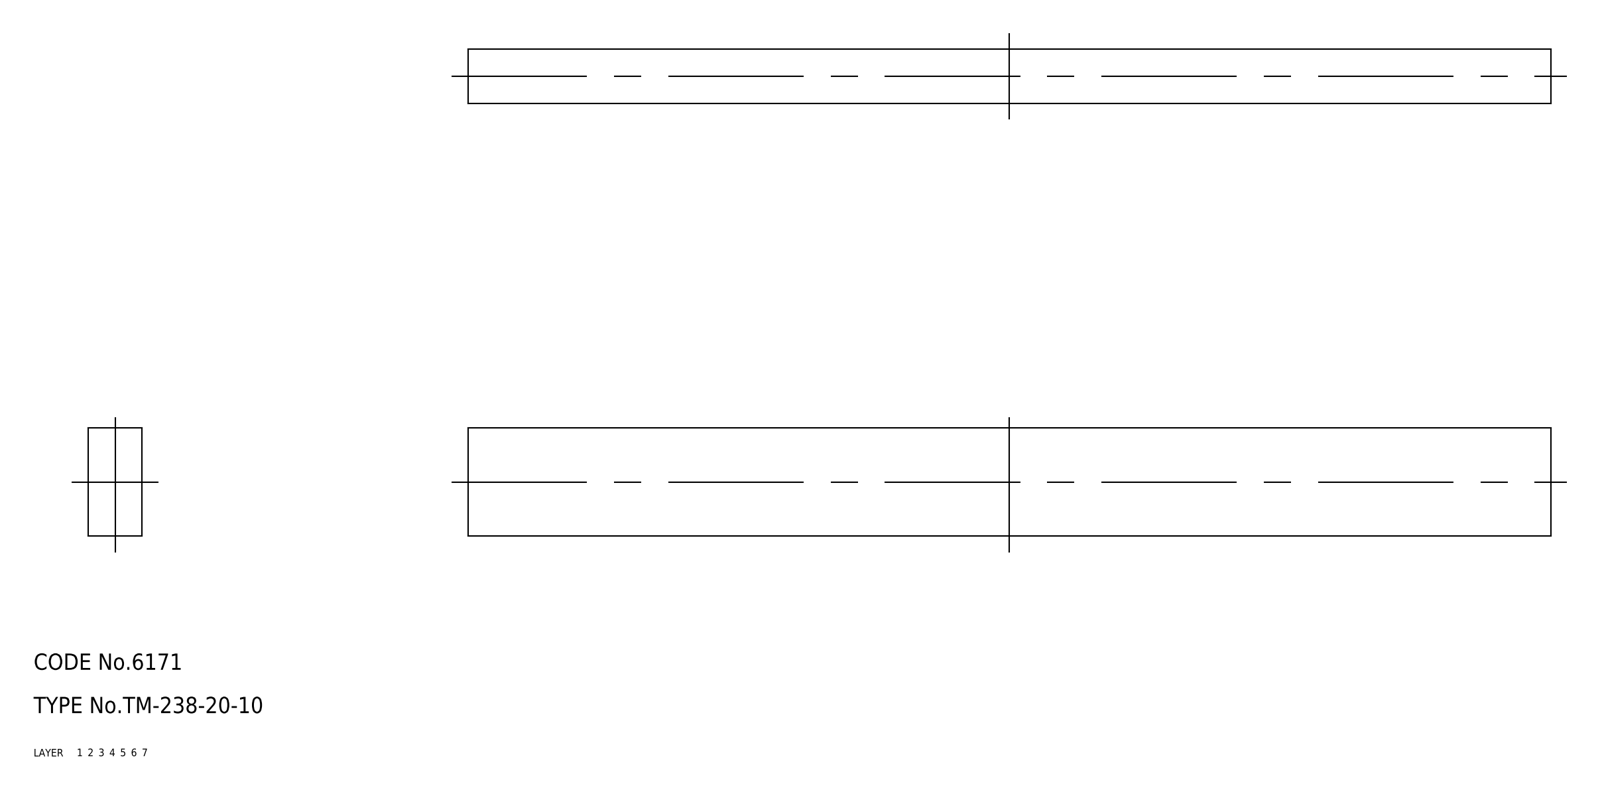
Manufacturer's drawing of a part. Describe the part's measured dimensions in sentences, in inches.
The part is named "rubber foam". Its 3-D file was written by "CADfix (AUTOMOTIVE_DESIGN)". It is 1 solid with 6 faces: 0 planar, 0 cylindrical and 6 other. Overall it measures 7.874 by 0.787 by 0.394 inches. Its volume is 2.441 cubic inches and its surface area 19.22 square inches.
